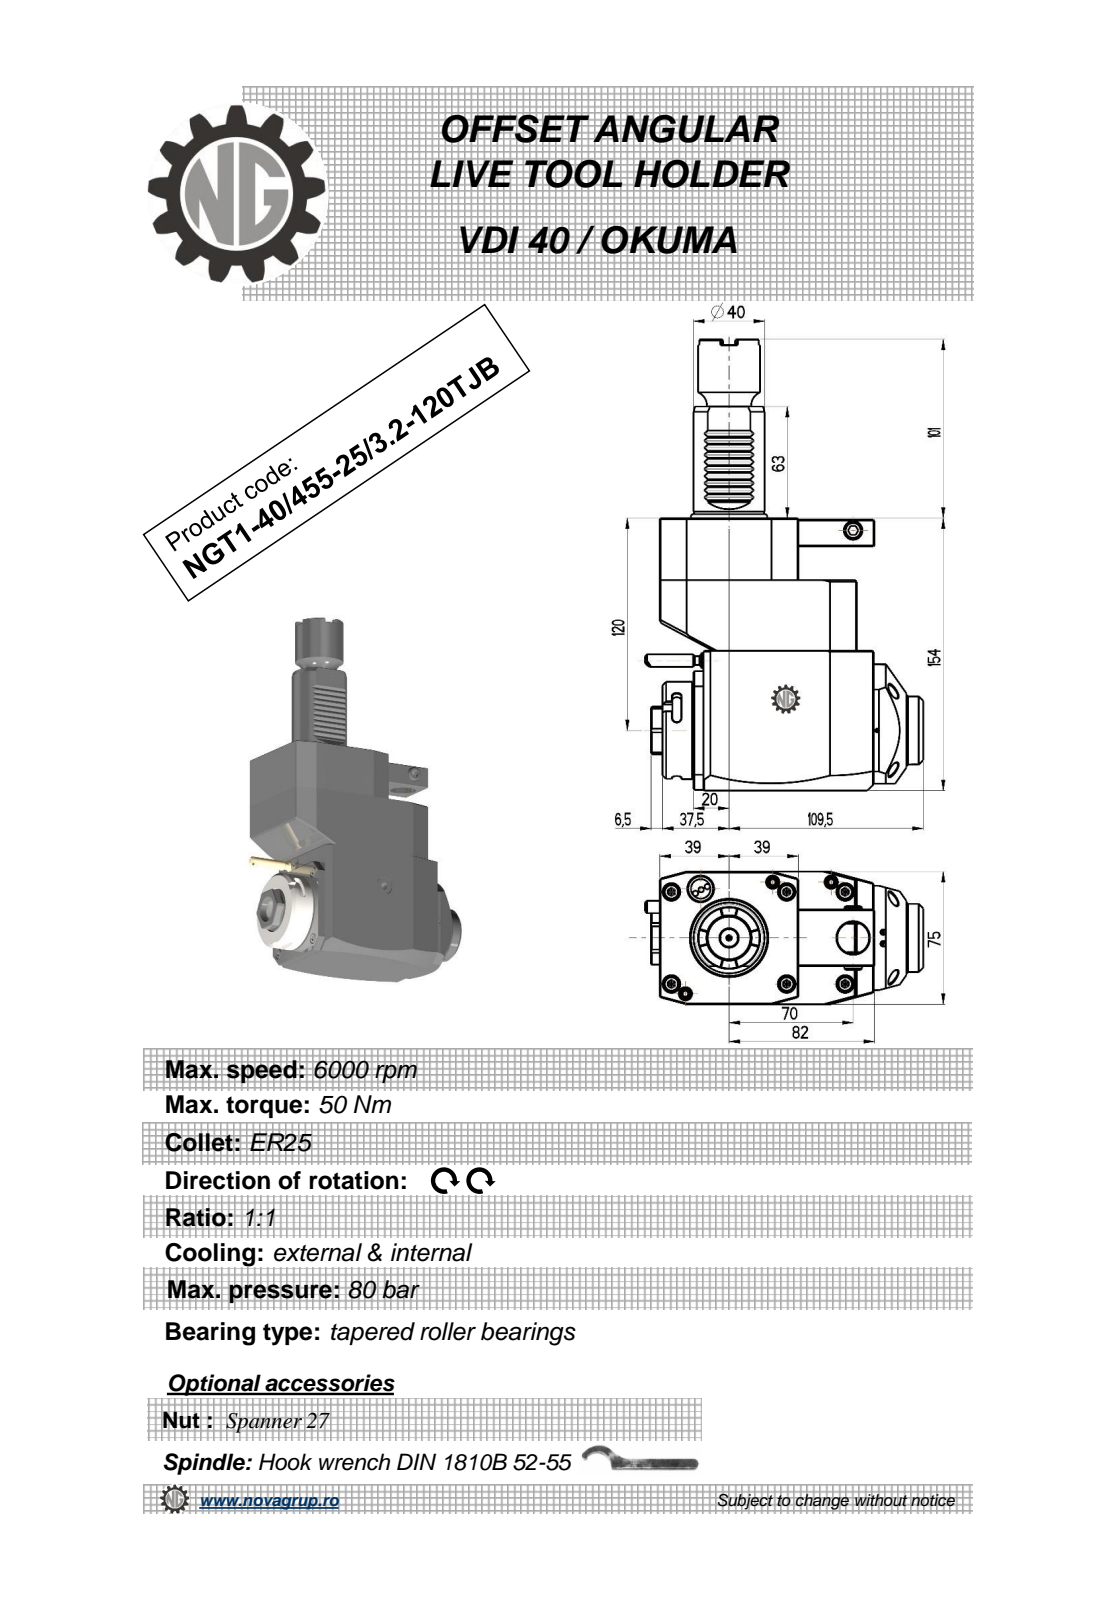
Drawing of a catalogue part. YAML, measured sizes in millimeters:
part_name: "NGT1_40_455_25_3_2_120TJB"
step_written_by: "PRO/ENGINEER BY PARAMETRIC TECHNOLOGY CORPORATION, 2010280 (CONFIG_CONTROL_DESIGN)"
units: millimeters
bodies: {solids: 1, faces: 379, planar: 199, cylindrical: 72, other: 108}
overall_size: [255, 156.83, 75]
volume: 1316000
surface_area: 95369
round_holes:
  - {diameter: 18, count: 2}
  - {diameter: 2.5, count: 1}
  - {diameter: 3, count: 1}
  - {diameter: 9.5, count: 1}
  - {diameter: 25, count: 1}
round_bosses_or_shafts:
  - {diameter: 8.96, count: 2}
  - {diameter: 55, count: 1}
  - {diameter: 48, count: 1}
  - {diameter: 40, count: 1}
  - {diameter: 38.5, count: 1}
  - {diameter: 35, count: 1}
  - {diameter: 10, count: 1}
  - {diameter: 7, count: 1}
partial_cylinders:
  - {radius: 0.3, count: 10}
  - {radius: 2.5, count: 6}
  - {radius: 180, count: 2}
  - {radius: 0.5, count: 1}
  - {radius: 4.25, count: 1}
  - {radius: 15, count: 1}
  - {radius: 24.5, count: 1}
  - {radius: 37.5, count: 1}
face_to_face_distances: [75, 154, 19, 119, 59, 111, 92, 35, 17.5, 53.5]
hole_center_spacings: [43.2, 70, 75.07, 112.5]
